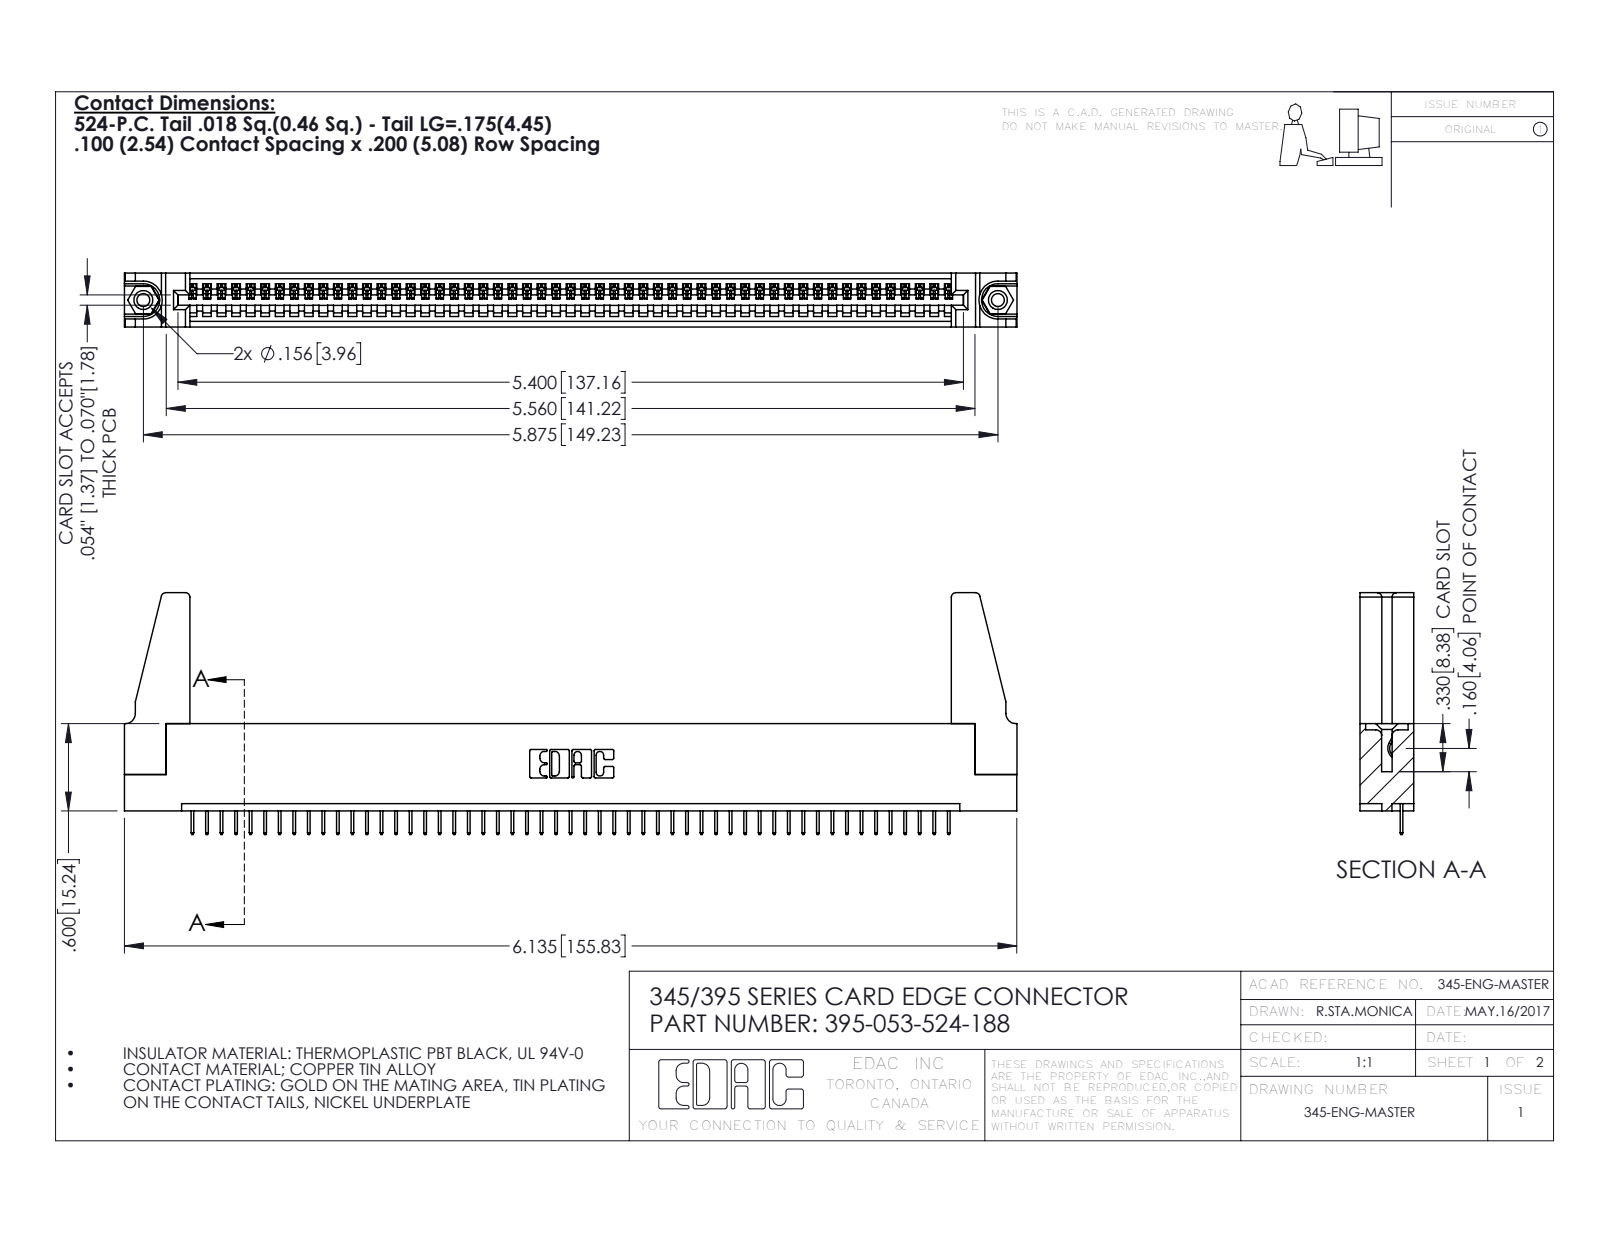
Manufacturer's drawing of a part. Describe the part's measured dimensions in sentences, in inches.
The part is named "395-053-524-188; 345-292-001_345-293-124; 345-220-078_345-220-088; 345 Part_Flush Mounting Lugs - 0.156 Dia-TH (+1 more)". Its 3-D file was written by "SolidWorks 2016 (CONFIG_CONTROL_DESIGN)". It is 58 solids with 3536 faces: 2590 planar, 930 cylindrical and 16 other. Overall it measures 6.136 by 1.662 by 0.37 inches. Its volume is 1.095 cubic inches and its surface area 34.29 square inches. Round holes: 2 of diameter 0.089, 2 of diameter 0.125, 2 of diameter 0.156, 1 of diameter 0.064. Round bosses or shafts: 2 of diameter 0.155. Partial cylindrical surfaces (rounded edges, fillets, slot ends): 106 of radius 0.006, 22 of radius 0.01, 8 of radius 0.03, 6 of radius 0.007, 6 of radius 0.031, 3 of radius 0.026, 2 of radius 0.031, 2 of radius 0.04. The main face-to-face distances are 0.072, 0.298, 0.37, 0.2, 0.098, 0.272, 0.025, 0.225, 0.072, 0.149. The hole center spacings are 0.27, 5.639, 5.875.
